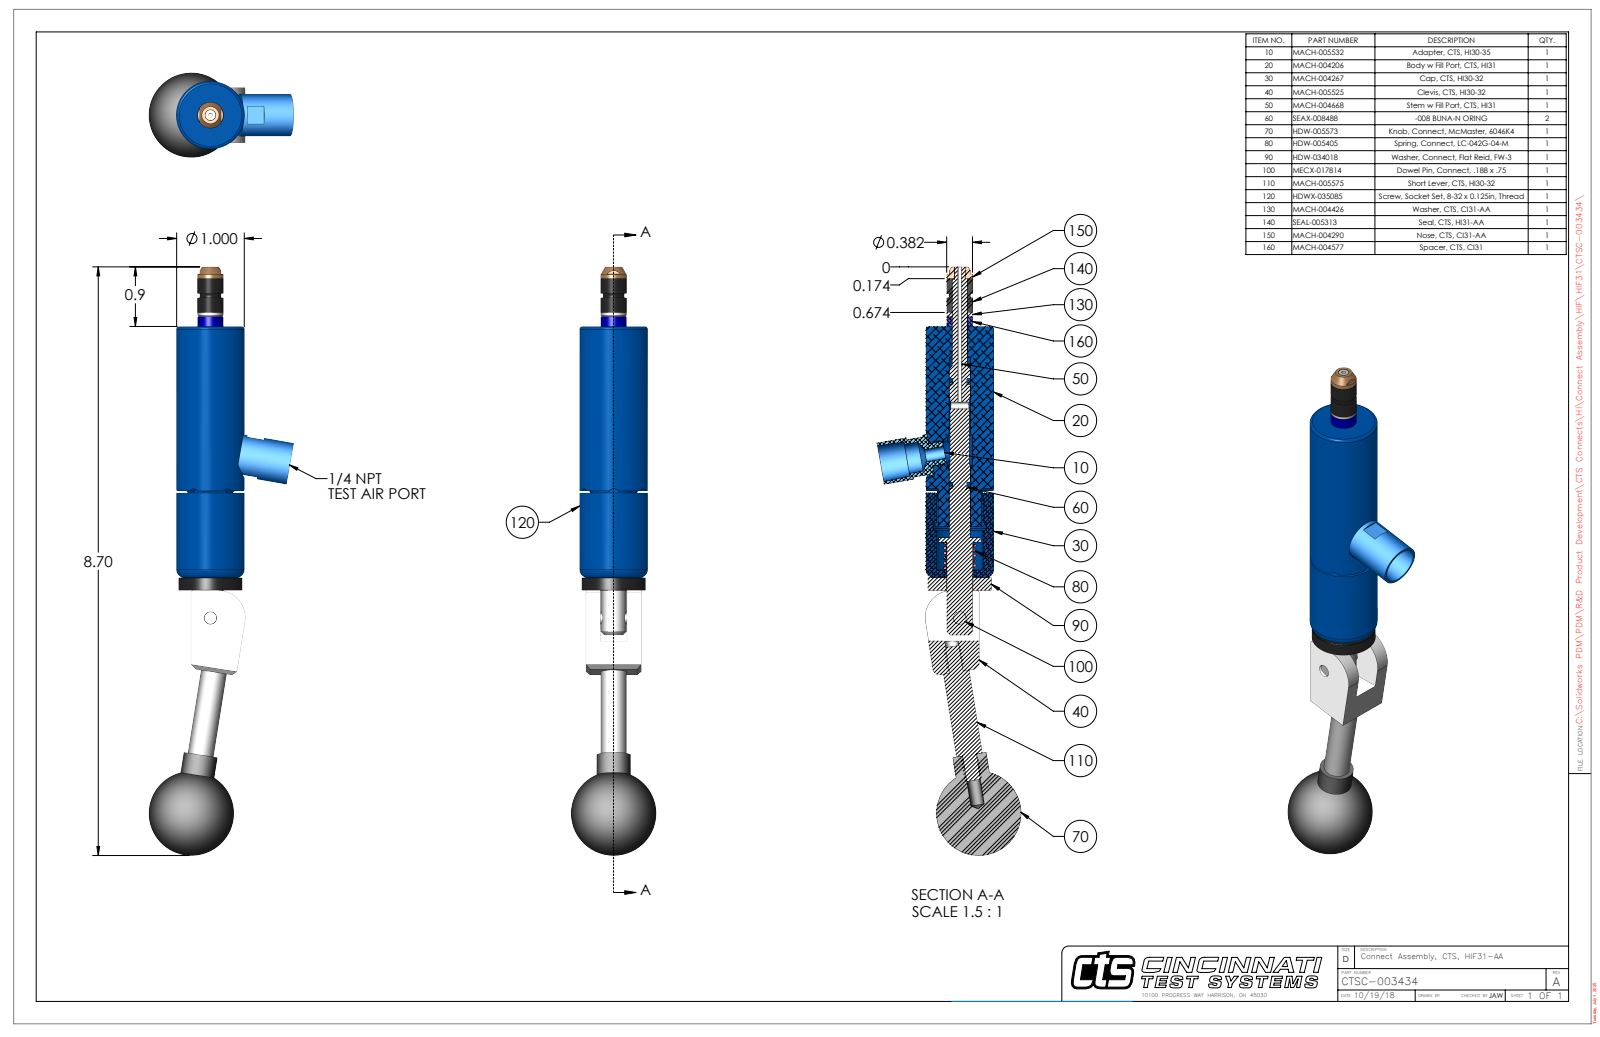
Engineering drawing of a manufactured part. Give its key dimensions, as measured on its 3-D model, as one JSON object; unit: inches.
{"part_name": "CTSC-003434", "step_written_by": "SolidWorks 2023 (AUTOMOTIVE_DESIGN)", "units": "inches", "bodies": {"solids": 10, "faces": 284, "planar": 98, "cylindrical": 122, "other": 64}, "overall_size": [8.704, 2.128, 1.25], "volume_in3": 4.958, "surface_area_in2": 37.34, "round_holes": [[0.201, 2], [0.063, 1], [0.104, 1], [0.109, 1], [0.136, 1], [0.15, 1], [0.159, 1], [0.187, 1], [0.189, 1], [0.218, 1], [0.228, 1], [0.229, 1]], "round_bosses_or_shafts": [[1, 1], [0.936, 1], [0.62, 1], [0.5, 1], [0.384, 1], [0.381, 1], [0.38, 1], [0.379, 1]], "partial_cylinders_radius": [[0.093, 6], [0.029, 2], [0.325, 1], [0.4, 1], [0.458, 1], [0.477, 1]], "face_to_face_distances": [0.21, 0.602, 0.812, 0.187, 3.713, 3.901, 0.391, 2.46, 1.253, 1.441], "hole_center_spacings": [0.599, 1.658, 2.252]}
